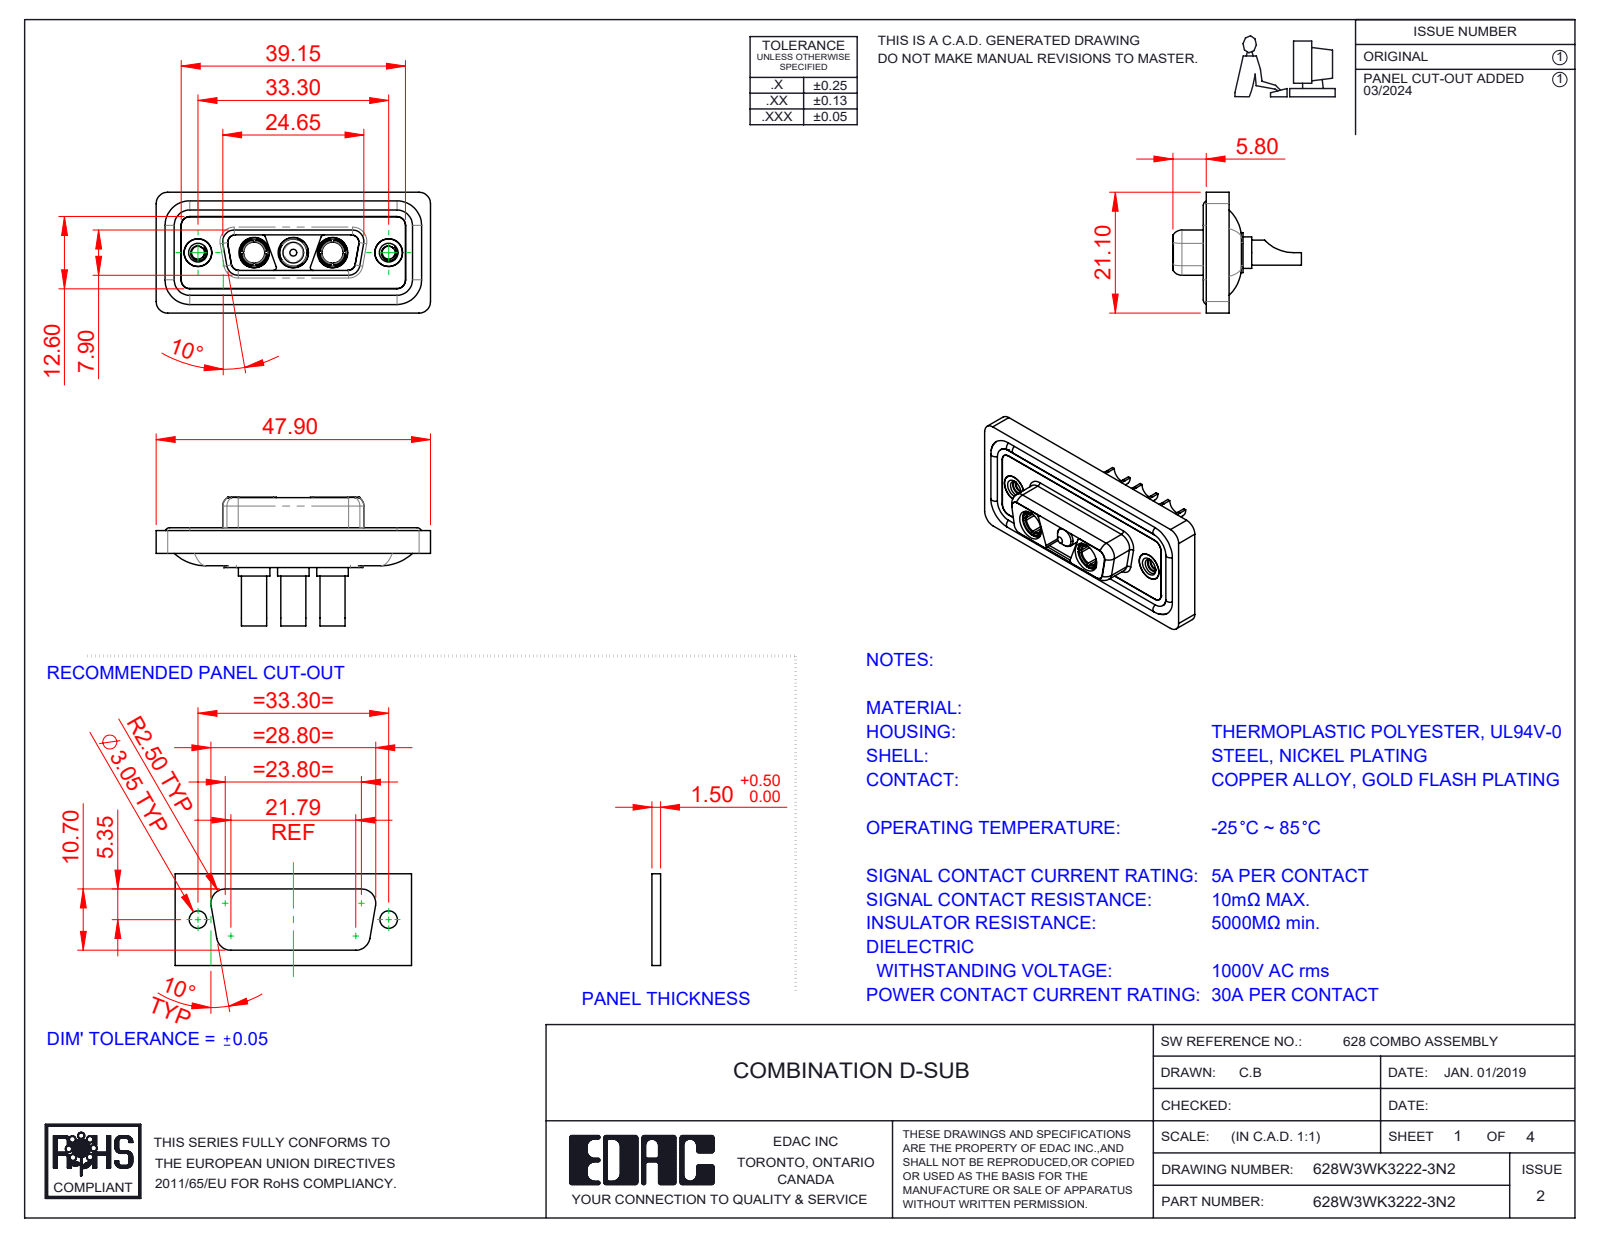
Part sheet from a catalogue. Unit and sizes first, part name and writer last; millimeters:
Units: millimetres
Overall size (bounding box): 47.9 × 22.45 × 21.1
Round holes (diameter × count): ⌀4.85 ×5, ⌀3.5 ×3, ⌀5.3 ×3, ⌀2.26 ×2, ⌀3.7 ×2, ⌀4 ×2, ⌀4.05 ×2, ⌀5 ×2
Round bosses / shafts (diameter × count): ⌀1.6 ×4, ⌀5.5 ×3, ⌀5.2 ×3, ⌀4.75 ×3, ⌀4.4 ×3, ⌀3.75 ×3, ⌀4.96 ×2, ⌀4.95 ×2
Partial cylindrical surfaces — rounded edges, fillets, slot ends (radius × count): R1.5 ×22, R2 ×20, R1.35 ×12, R0.5 ×8, R1.6 ×8, R0.25 ×4, R0.6 ×4, R0.65 ×4
Main face-to-face distances: 0.4, 1.6, 0.5, 1.1, 2.9, 1.8, 5.65, 7.05, 5.35, 6.6
Hole centre spacings: 6.85, 9.8, 16.65, 23.5, 13.7, 33.3
Volume: 5 950 mm³ · Surface area: 9 827 mm²
Bodies: 13 solids, 601 faces (187 planar, 267 cylindrical, 147 other)
Part name (STEP PRODUCT): 628Combo Shell Rear_15 Contacts; Power Pin_30A SC; 628W3WK3222-3N2; 628Combo Housing_3WK3 (+4 more)
STEP written by: SolidWorks 2023 (CONFIG_CONTROL_DESIGN)
